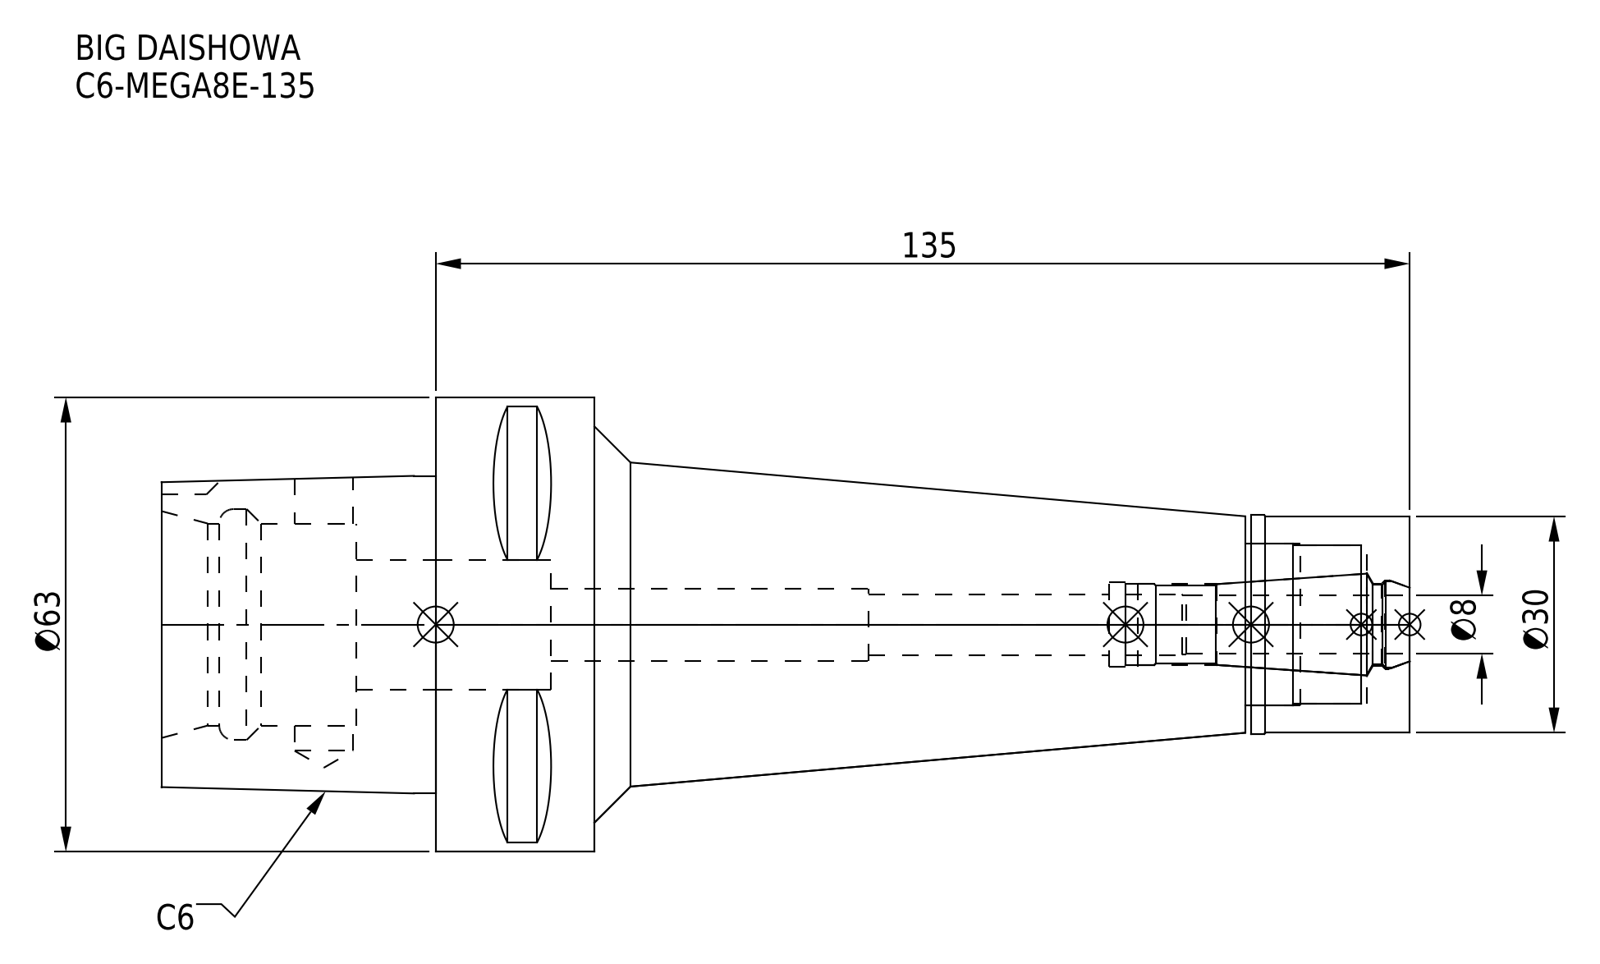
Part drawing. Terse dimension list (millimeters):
name: DXF_TEMP_ASSY_ASM_4_ASM.stp; C6-MEGA8E-135-080-FreeParts; C6-MEGA8E-135-080.stp; C6-MEGA8E-135 (+3 more)
written by: SolidWorks 2019 (CONFIG_CONTROL_DESIGN)
unit: mm
bodies: 2 solids, 100 faces (37 planar, 39 cylindrical, 24 other)
size: 173 × 63 × 63
volume: 207 150 mm³; area: 38 870 mm²
holes: 1× ⌀8.1, 1× ⌀8.4, 1× ⌀10, 1× ⌀11.2, 1× ⌀11.4, 1× ⌀11.8, 1× ⌀12.3, 1× ⌀18, 1× ⌀22, 1× ⌀22.5, 1× ⌀28, 1× ⌀32
bosses: 1× ⌀63, 1× ⌀30.3, 1× ⌀30
rounds: 1× R5
face distances: 113, 22, 135, 27, 38, 60, 173, 6, 16, 146
